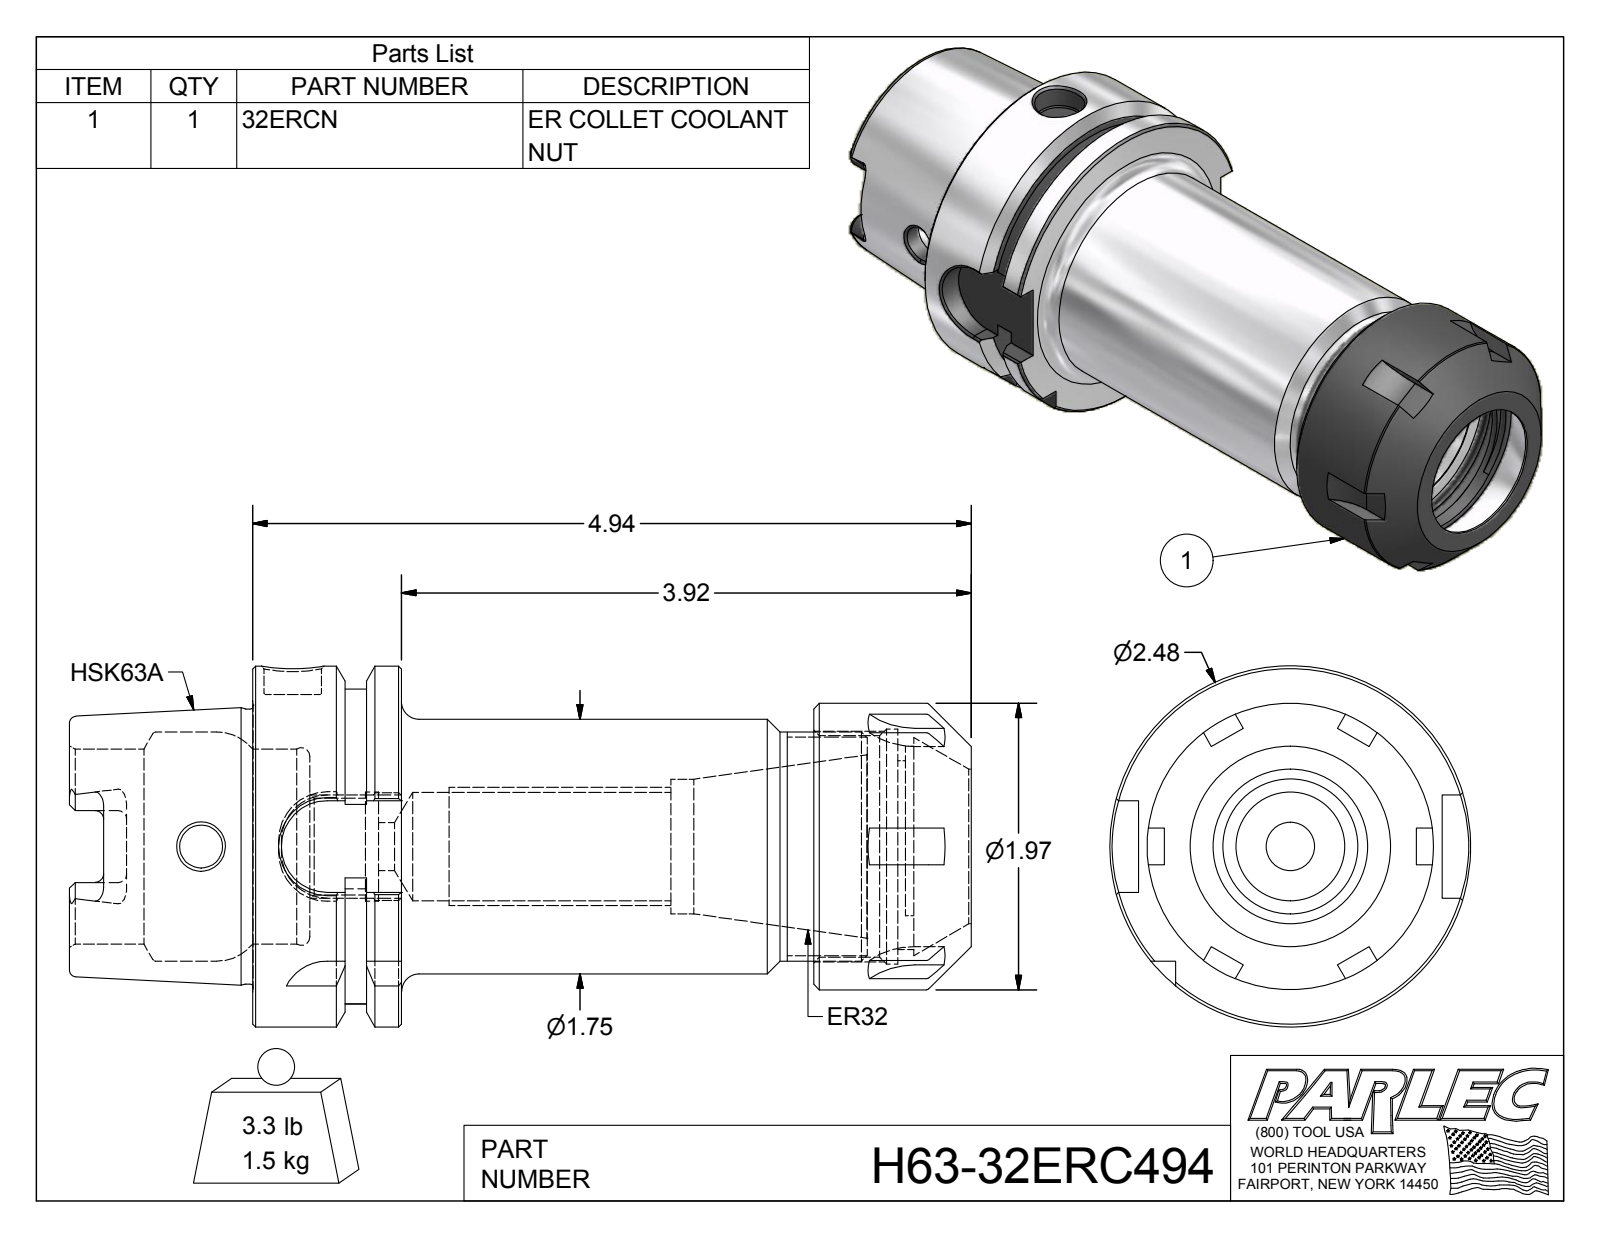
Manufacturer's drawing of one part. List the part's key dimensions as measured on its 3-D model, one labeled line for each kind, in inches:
Part name (STEP PRODUCT): H63-32ERC494; 32ERCN; H63-32ER5-1
STEP written by: Autodesk Inventor 2012 (AUTOMOTIVE_DESIGN)
Units: inches
Bodies: 2 solids, 184 faces (75 planar, 48 cylindrical, 61 other)
Overall size (bounding box): 6.2 × 2.48 × 2.48
Volume: 11.57 in³ · Surface area: 75.04 in²
Round holes (diameter × count): ⌀0.295 ×1, ⌀0.331 ×1, ⌀0.394 ×1, ⌀0.666 ×1, ⌀0.745 ×1, ⌀0.749 ×1, ⌀0.925 ×1, ⌀1.063 ×1, ⌀1.299 ×1, ⌀1.339 ×1, ⌀1.522 ×1, ⌀1.575 ×1
Round bosses / shafts (diameter × count): ⌀2.48 ×1, ⌀1.969 ×1, ⌀1.891 ×1, ⌀1.75 ×1
Partial cylindrical surfaces — rounded edges, fillets, slot ends (radius × count): R0.059 ×6, R0.5 ×6, R0.113 ×4, R0.315 ×4, R0.689 ×1, R1.083 ×1
Main face-to-face distances: 1.024, 0.394, 0.63, 3.857, 3.464, 2.834, 4.436, 4.043, 3.413, 0.579
Hole centre spacings: 0.059
